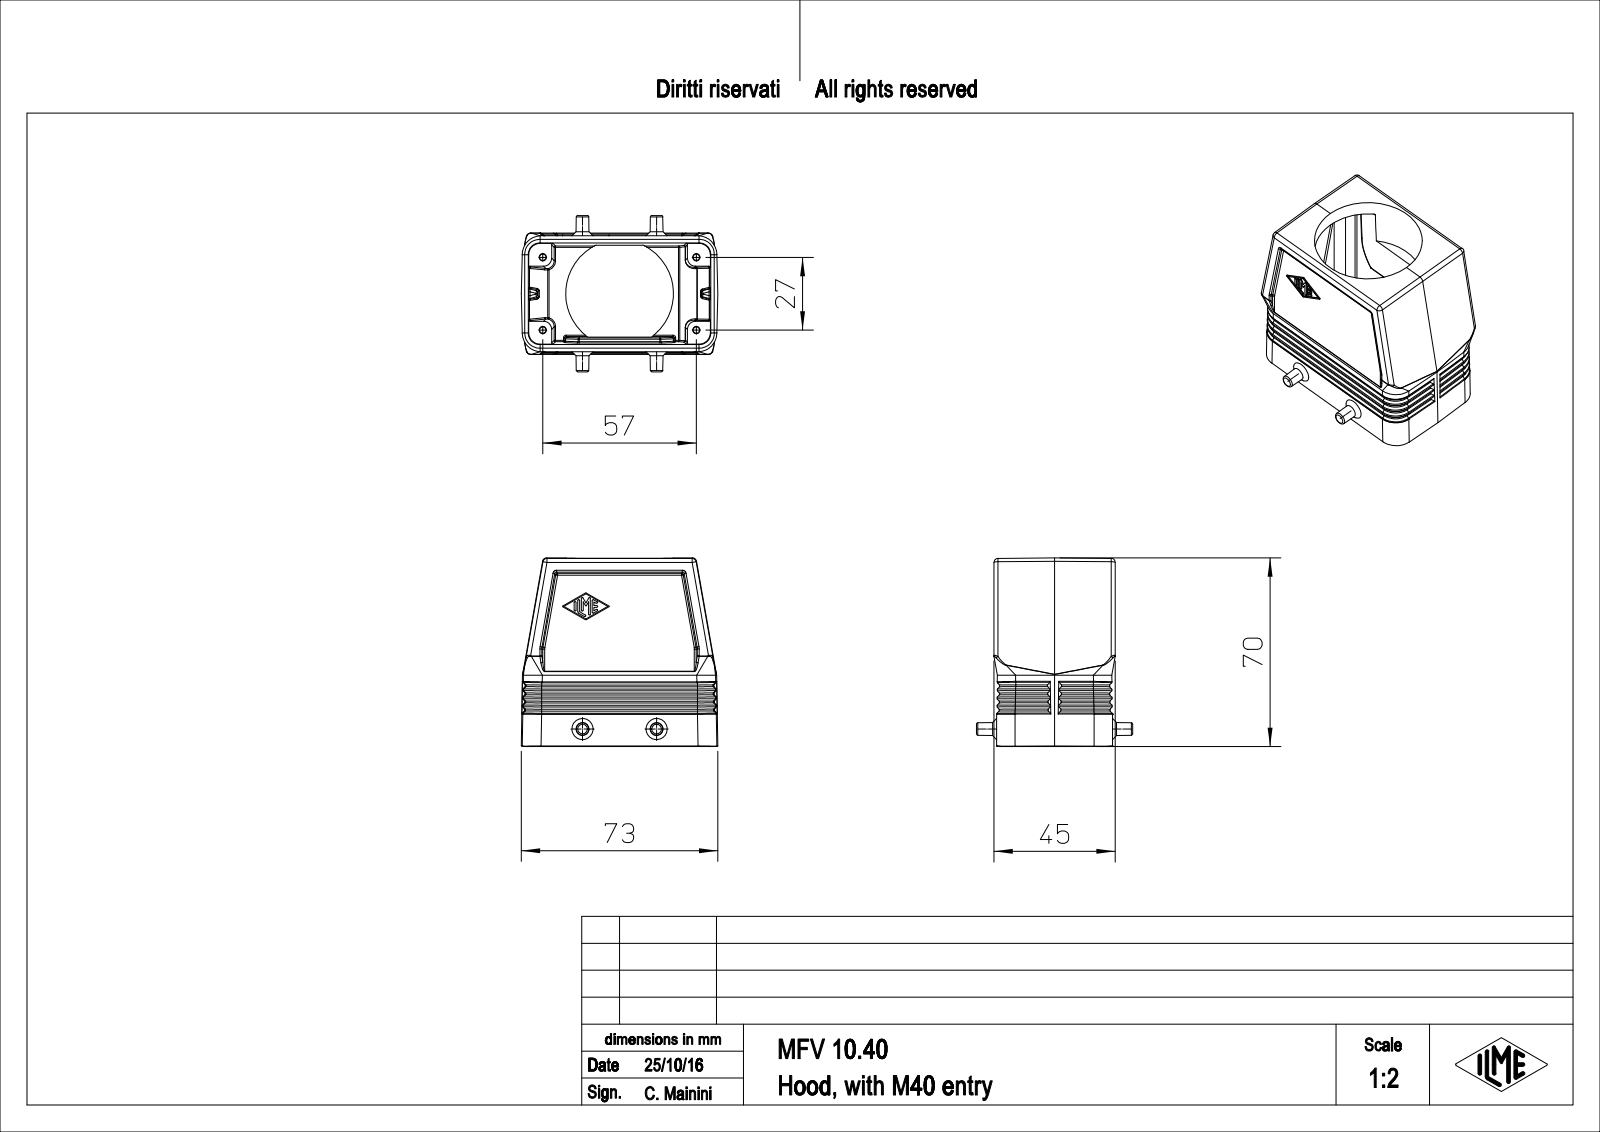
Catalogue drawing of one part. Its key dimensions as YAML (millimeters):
part_name: "MFV_10.40"
step_written_by: "PTC Creo Elements/Direct Modeling 19.0E 27-Jun-2016 (C) Parametric Technology GmbH (AUTOMOTIVE_DESIGN)"
units: millimeters
bodies: {solids: 1, faces: 354, planar: 141, cylindrical: 71, other: 142}
overall_size: [72.99, 70, 58]
volume: 62102
surface_area: 32308
round_holes:
  - {diameter: 2.75, count: 4}
  - {diameter: 40, count: 1}
round_bosses_or_shafts:
  - {diameter: 4.59, count: 2}
partial_cylinders:
  - {radius: 0.5, count: 17}
  - {radius: 1.5, count: 10}
  - {radius: 7, count: 8}
  - {radius: 3, count: 4}
  - {radius: 4.2, count: 4}
  - {radius: 6, count: 4}
  - {radius: 20, count: 1}
face_to_face_distances: [43, 8.5, 2, 1.91, 44, 1, 4, 45, 6, 11.35]
hole_center_spacings: [31.54, 27, 57, 63.07]
